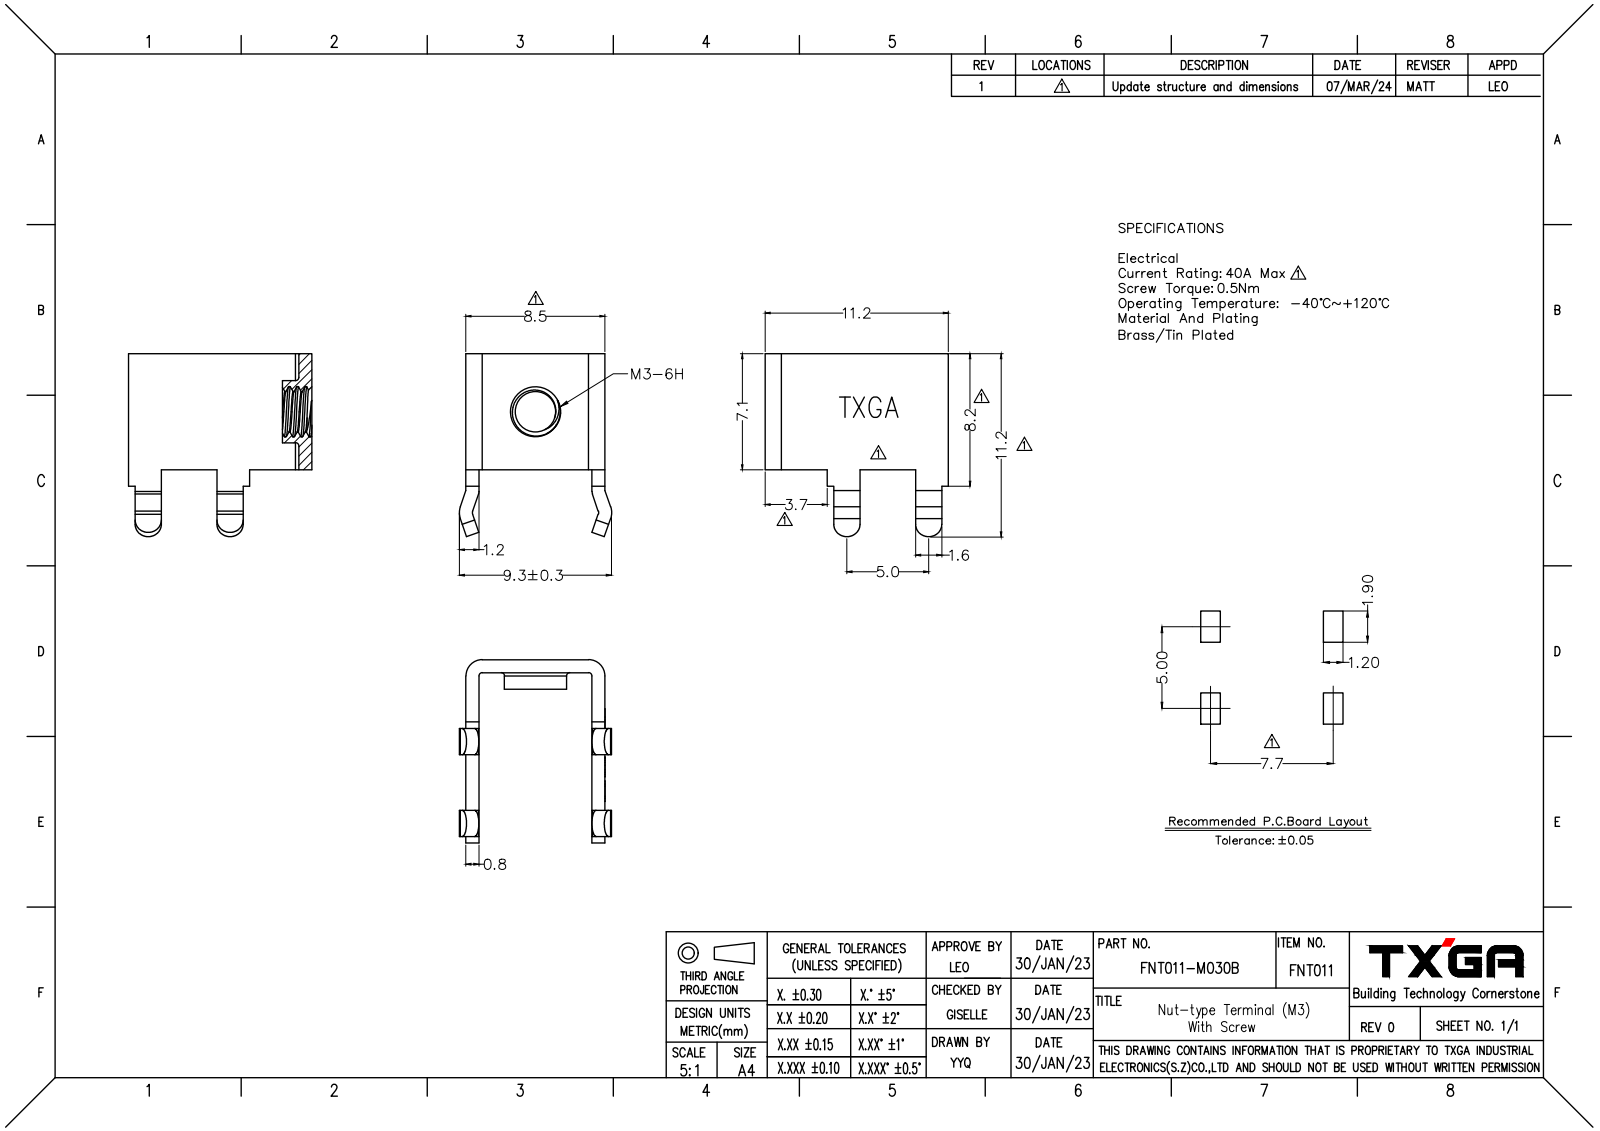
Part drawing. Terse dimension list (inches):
name: MFE04311-T3
written by: CREO PARAMETRIC BY PTC INC, 2021023 (AUTOMOTIVE_DESIGN)
unit: in
bodies: 1 solid, 134 faces (107 planar, 20 cylindrical, 7 other)
size: 0.512 × 0.453 × 0.328
volume: 0.012 in³; area: 0.966 in²
holes: 1× ⌀0.098
bosses: 1× ⌀0.161
rounds: 2× R0.02, 2× R0.03, 2× R0.039
face distances: 0.031, 0.295, 0.264, 0.327, 0.039, 0.059, 0.197, 0.453, 0.421, 0.276
